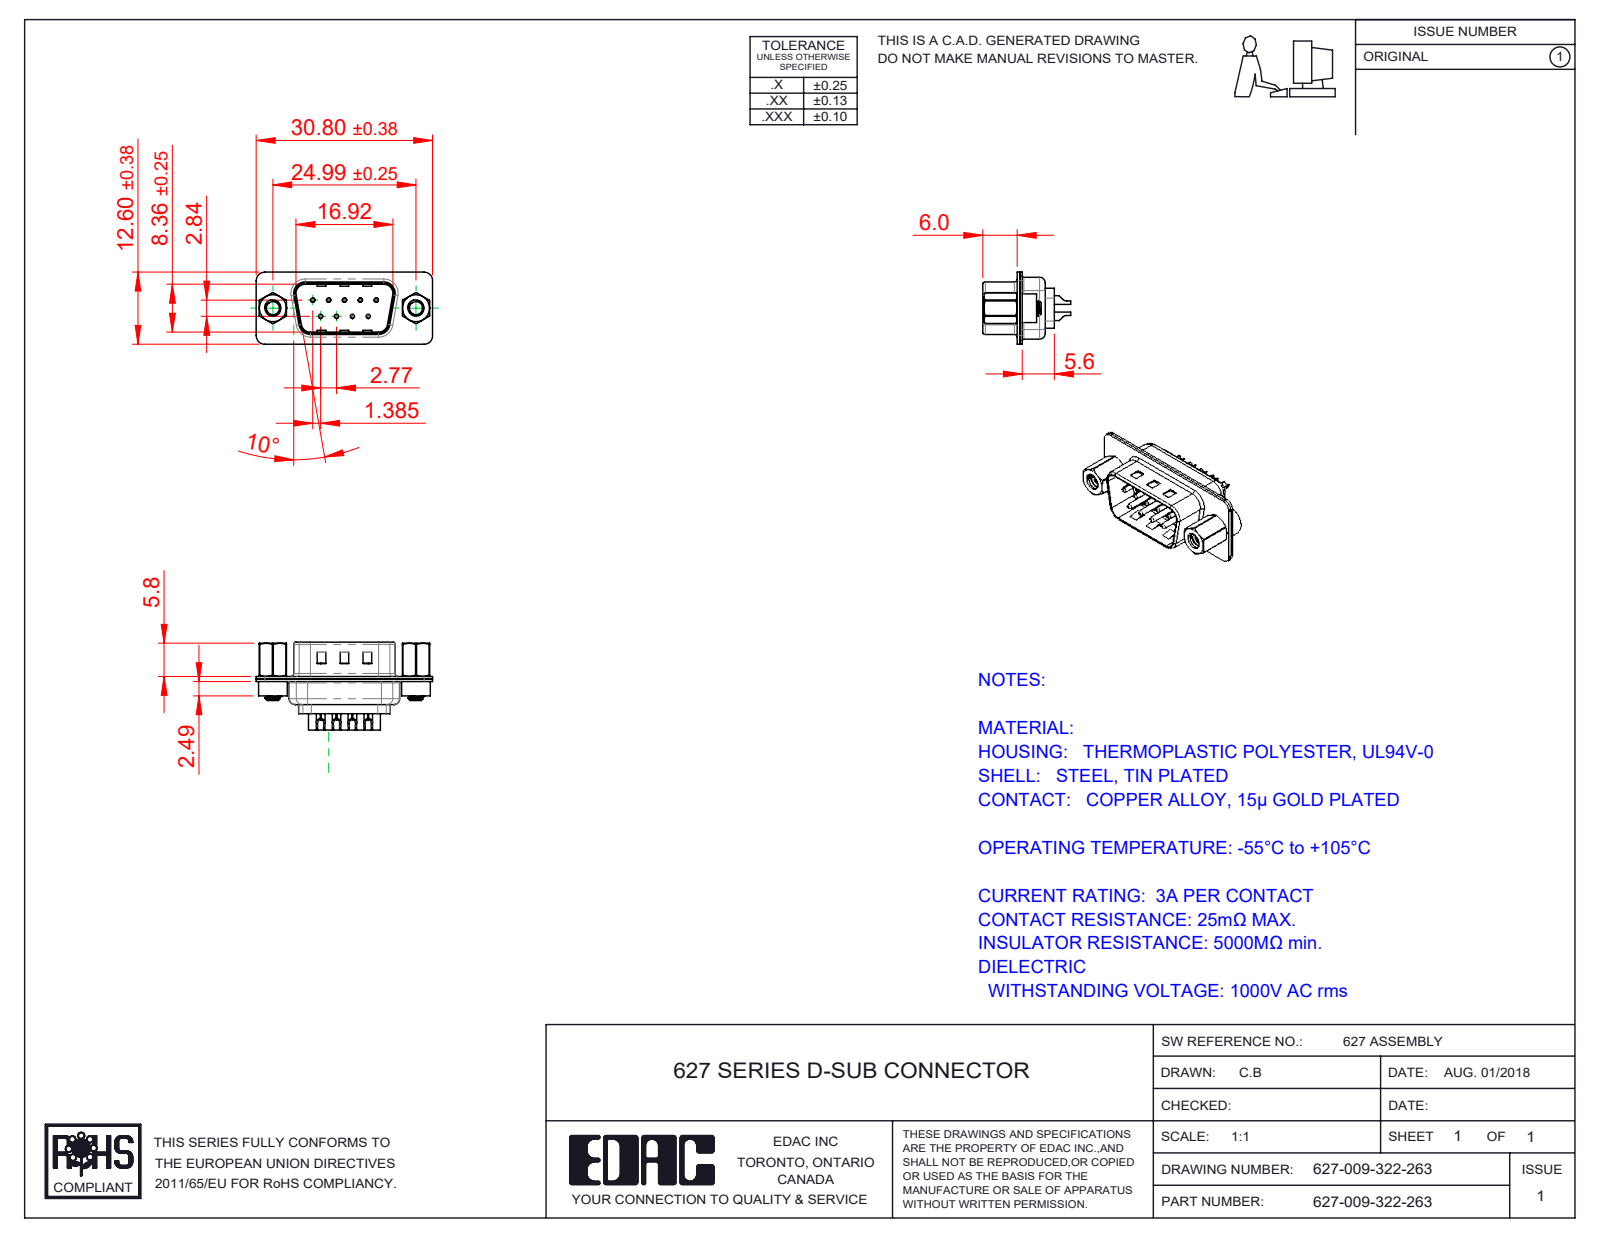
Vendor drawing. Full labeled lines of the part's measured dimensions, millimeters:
Part name (STEP PRODUCT): 627 4-40 Threaded Rivet; 627 Shell Front_09 Contacts; 627 Housing_09 LP; 627 4-40 Hex Standoff (+4 more)
STEP written by: SolidWorks 2020 (CONFIG_CONTROL_DESIGN)
Units: millimetres
Bodies: 16 solids, 1002 faces (255 planar, 460 cylindrical, 287 other)
Overall size (bounding box): 30.8 × 15.35 × 12.6
Volume: 1 523 mm³ · Surface area: 4 425 mm²
Round holes (diameter × count): ⌀0.35 ×9, ⌀1.1 ×9, ⌀1.6 ×9, ⌀2.26 ×2, ⌀2.29 ×2, ⌀4 ×2, ⌀4.8 ×2
Round bosses / shafts (diameter × count): ⌀2 ×9, ⌀1.5 ×9, ⌀0.75 ×9, ⌀5 ×2, ⌀4.9 ×2, ⌀2.79 ×2
Partial cylindrical surfaces — rounded edges, fillets, slot ends (radius × count): R1.5 ×18, R2 ×12, R0.5 ×8, R1.6 ×8, R1 ×6, R0.25 ×4, R0.6 ×4, R0.65 ×4
Main face-to-face distances: 0.45, 0.4, 0.9, 0.82, 9.58, 1.4, 8.76, 0.5, 1.5, 6.5
Hole centre spacings: 3.16, 2.77, 5.54, 5.03, 5.04, 8.31, 7.48, 7.49
